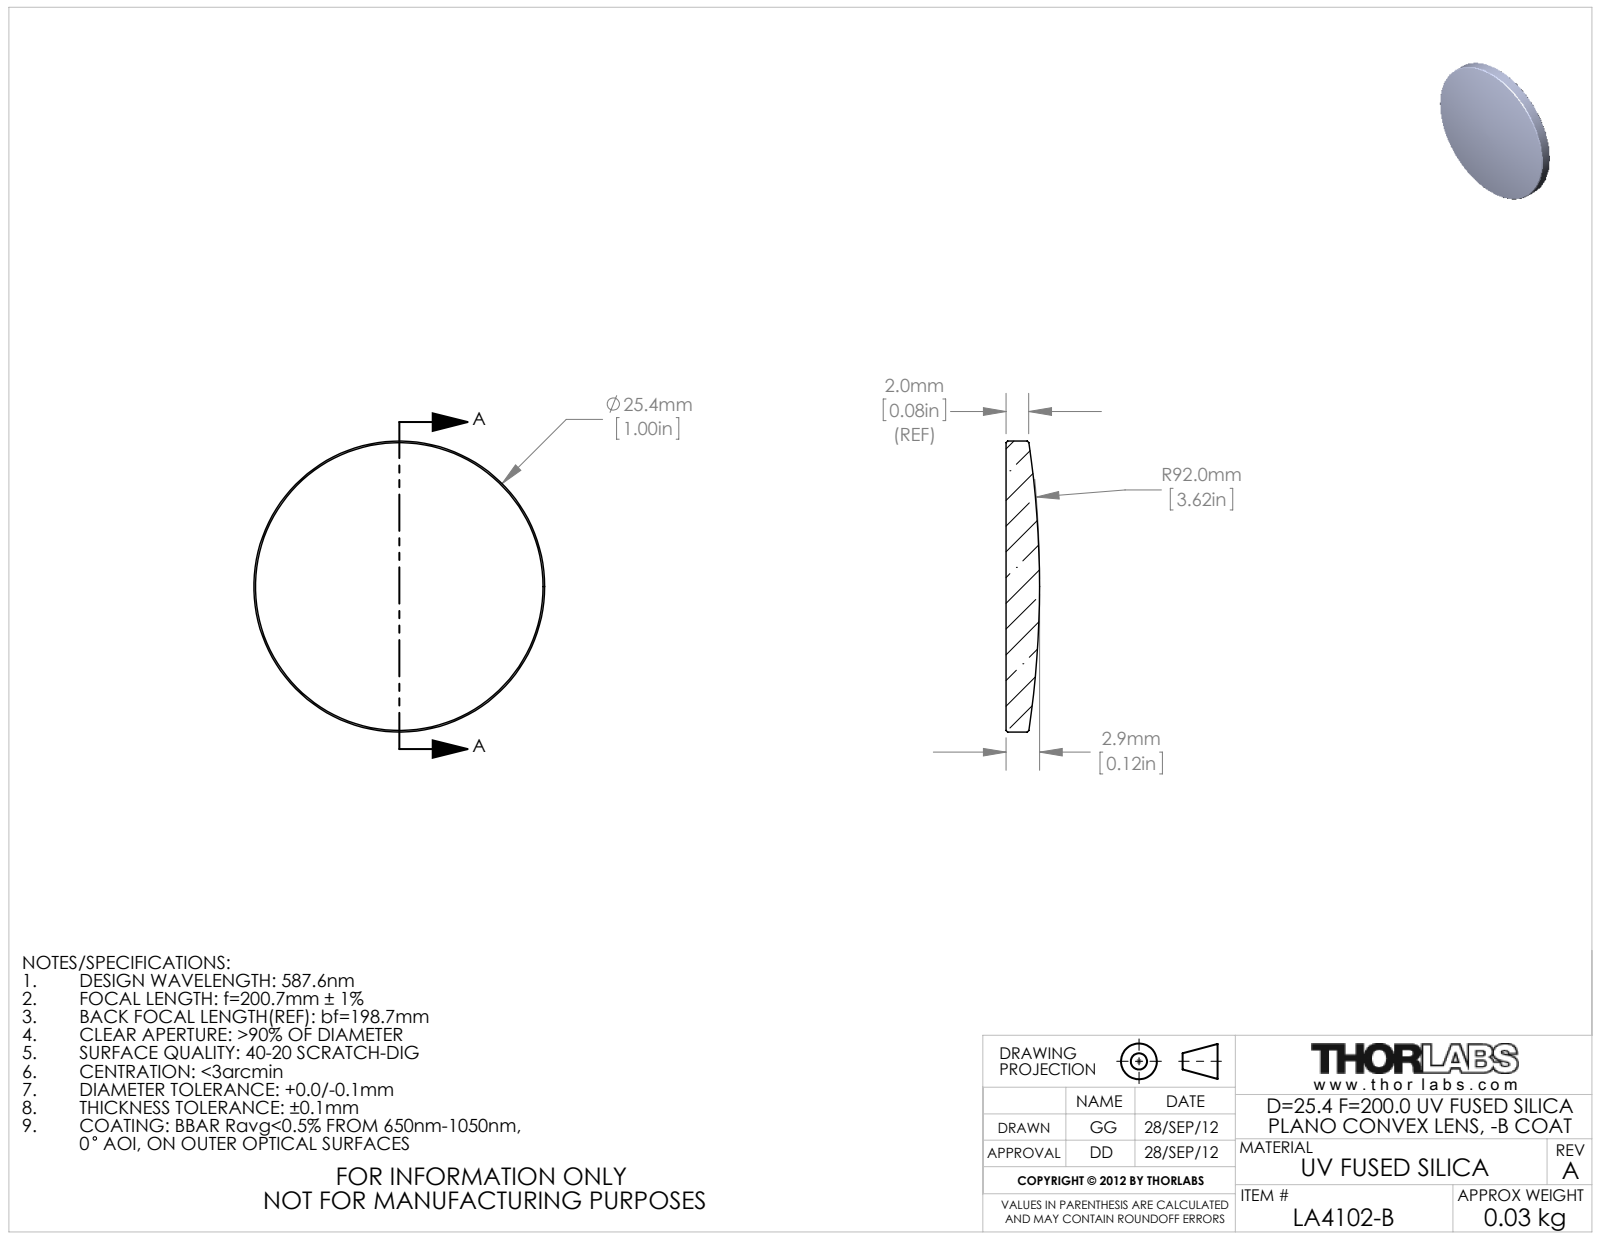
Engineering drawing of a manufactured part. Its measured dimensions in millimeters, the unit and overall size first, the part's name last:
Units: millimetres
Overall size (bounding box): 25.4 × 25.4 × 2.93
Round bosses / shafts (diameter × count): ⌀25.4 ×1
Volume: 1 237 mm³ · Surface area: 1 162 mm²
Bodies: 1 solid, 9 faces (1 planar, 2 cylindrical, 6 other)
Part name (STEP PRODUCT): 24988-E0W
STEP written by: SolidWorks 2011 (AUTOMOTIVE_DESIGN)
